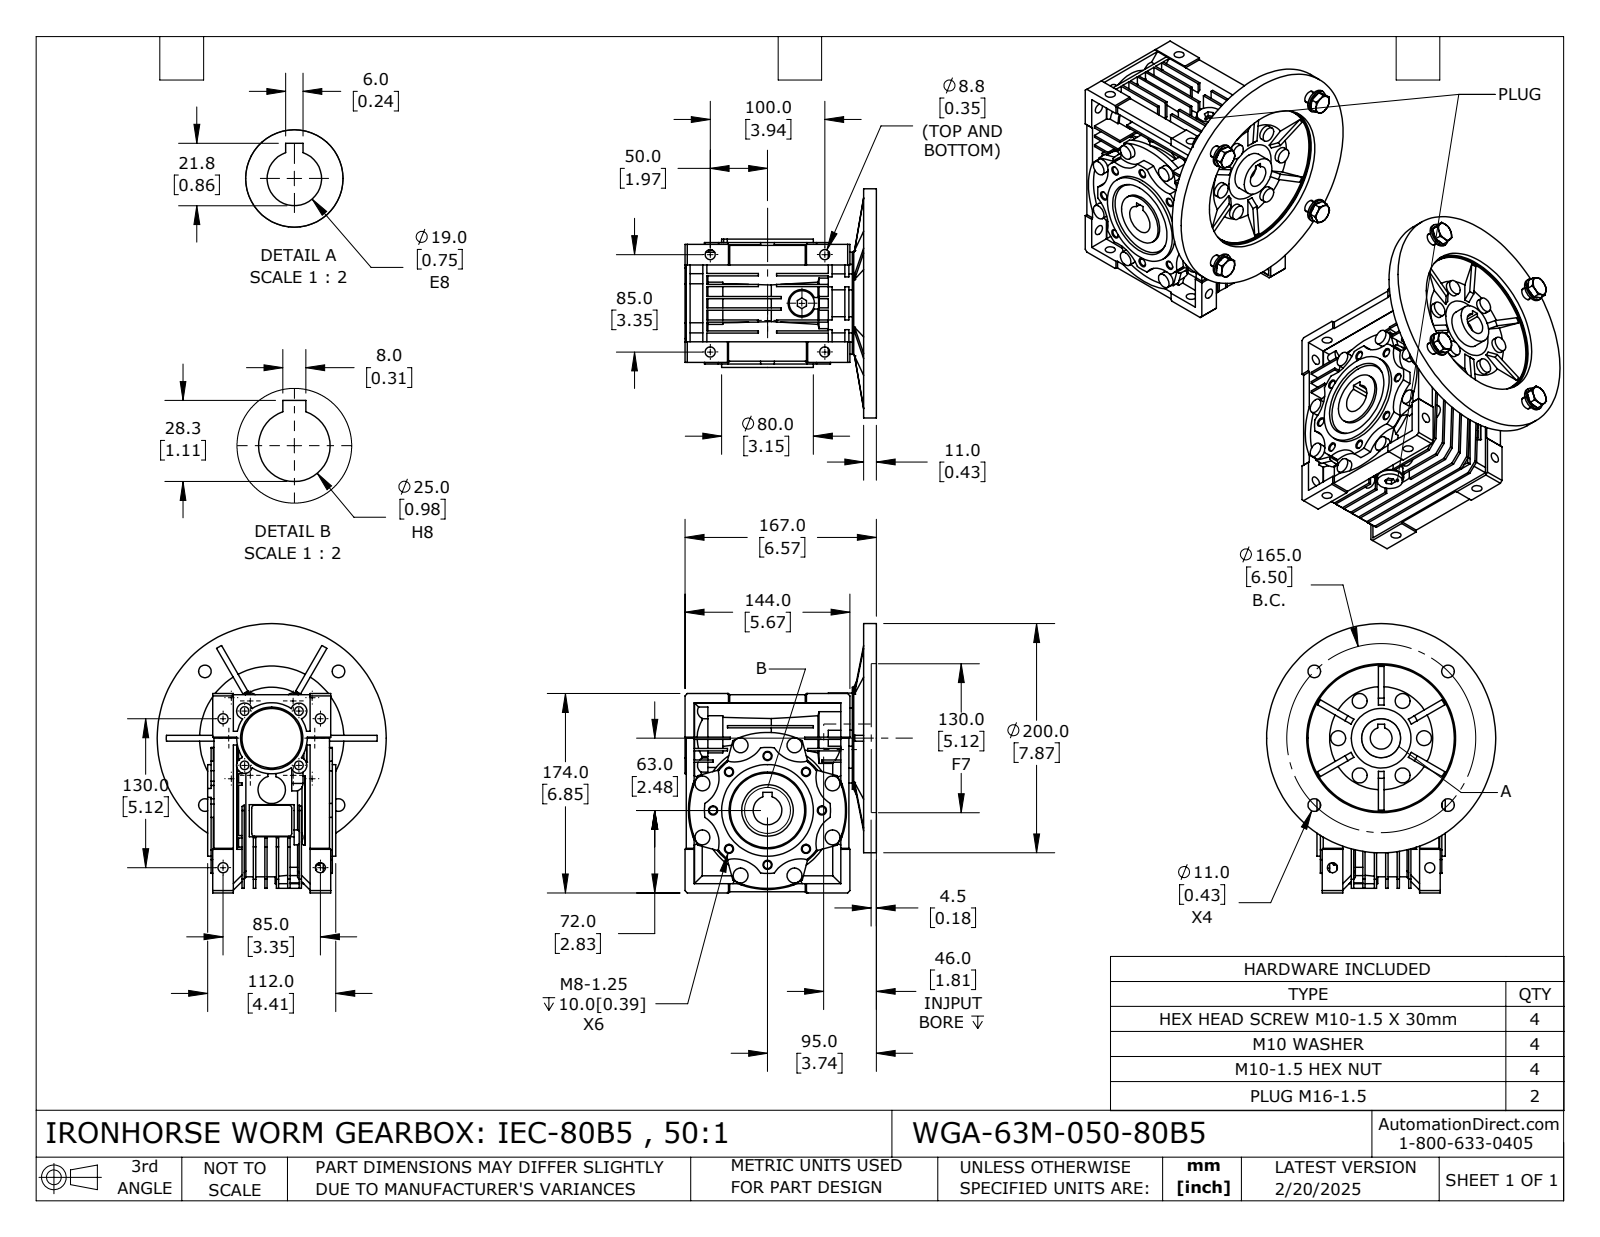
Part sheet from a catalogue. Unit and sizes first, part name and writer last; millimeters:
Units: millimetres
Overall size (bounding box): 235 × 200 × 167
Round holes (diameter × count): ⌀6.65 ×8, ⌀8.78 ×8, ⌀7.56 ×4, ⌀11 ×4, ⌀14.5 ×2, ⌀19 ×1, ⌀20 ×1, ⌀25 ×1, ⌀34 ×1, ⌀37 ×1, ⌀45 ×1, ⌀52 ×1
Round bosses / shafts (diameter × count): ⌀13 ×14, ⌀24 ×3, ⌀22 ×2, ⌀15.8 ×2, ⌀13.7 ×2, ⌀200 ×1, ⌀110 ×1, ⌀89 ×1
Partial cylindrical surfaces — rounded edges, fillets, slot ends (radius × count): R7 ×10, R27 ×8, R2.5 ×4, R8.35 ×1, R29.5 ×1, R30.5 ×1, R42 ×1, R46 ×1
Main face-to-face distances: 10, 8, 20, 2, 11, 30, 12, 7, 18, 40
Hole centre spacings: 36.36, 47.5, 67.18, 87.77, 89.05, 33.5, 47.38, 49
Volume: 2 010 000 mm³ · Surface area: 388 109 mm²
Bodies: 8 solids, 1285 faces (797 planar, 346 cylindrical, 142 other)
Part name (STEP PRODUCT): WGA-63M-050-80B5
STEP written by: SolidWorks 2024 (CONFIG_CONTROL_DESIGN)
